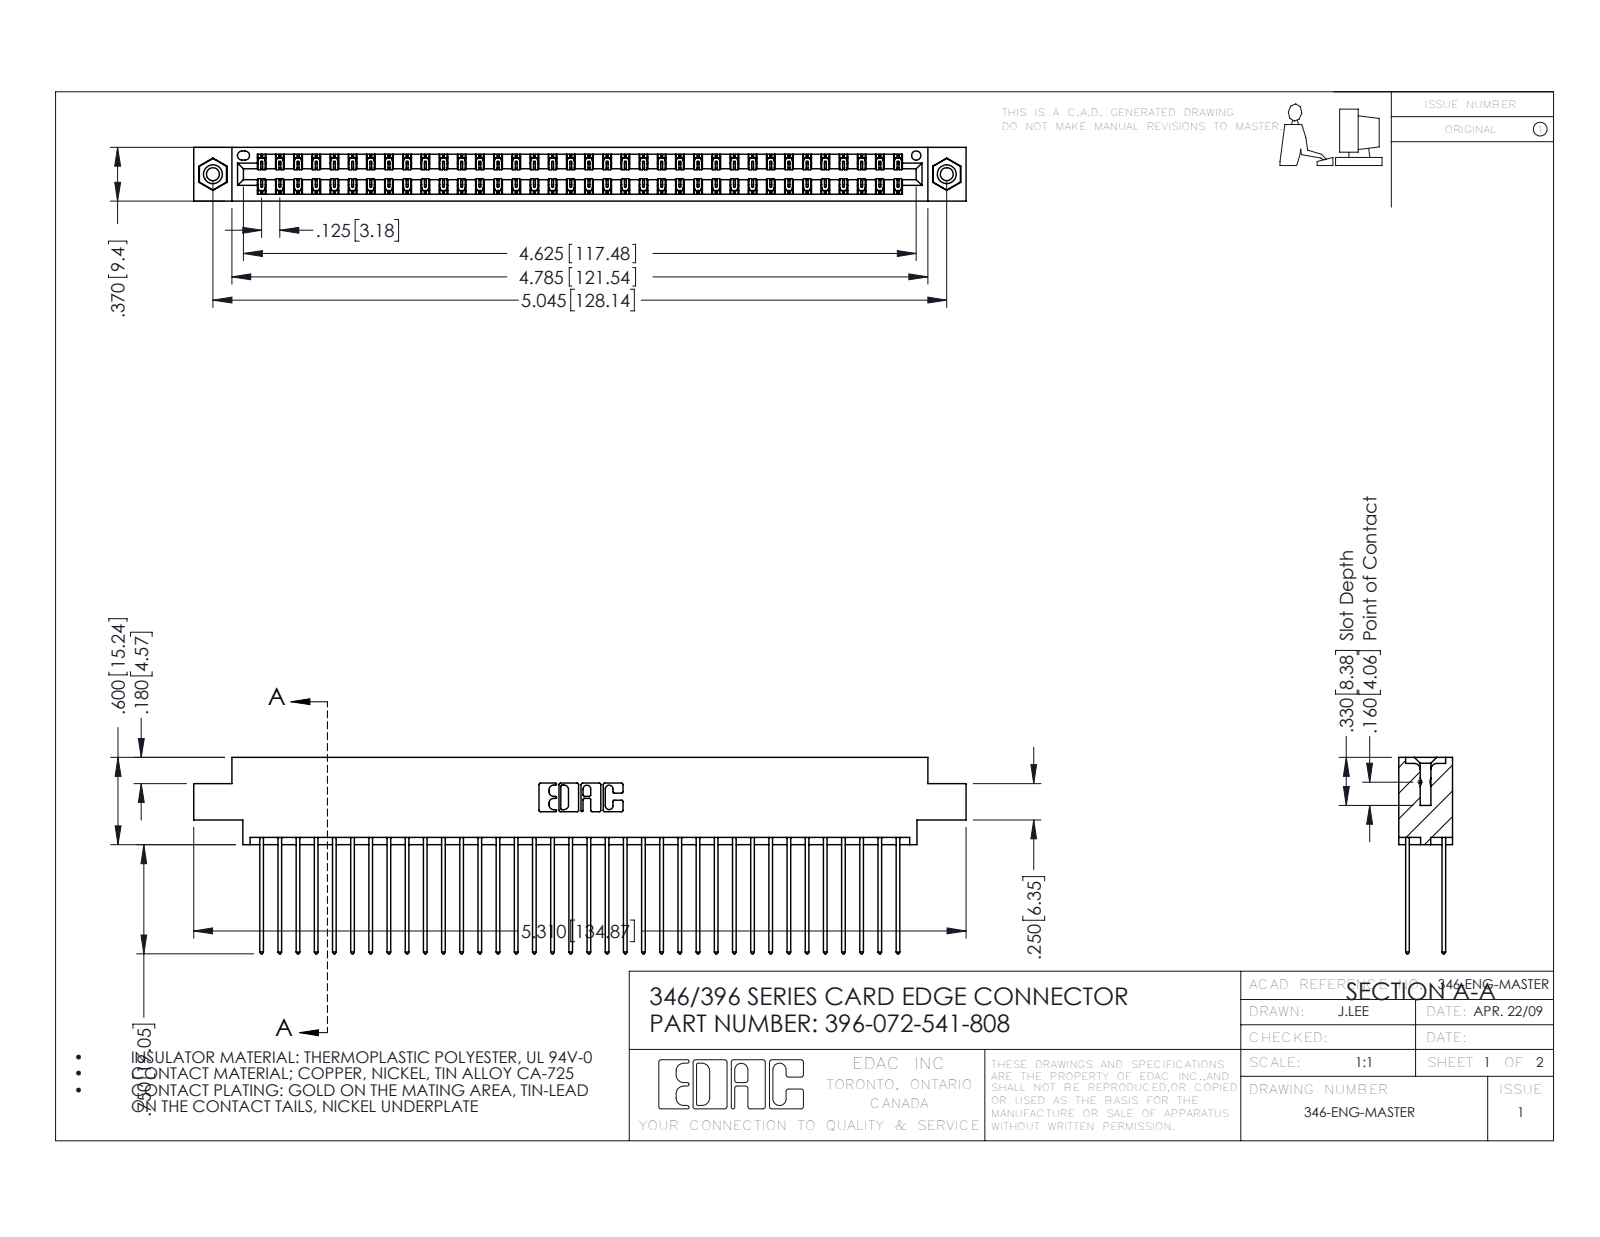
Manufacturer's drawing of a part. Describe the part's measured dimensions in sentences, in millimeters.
The part is named "396-072-541-808; 346 Part_0.170 Offset - 0.156 Dia-TI; 345-292-001_345-293-141; 345-250-001_345-250-003-102". Its 3-D file was written by "SolidWorks 2016 (CONFIG_CONTROL_DESIGN)". It is 75 solids with 3930 faces: 2632 planar, 1282 cylindrical and 16 other. Overall it measures 134.9 by 34.3 by 9.4 millimeters. Its volume is 13 400 cubic millimeters and its surface area 20 450 square millimeters. Round holes: 2 of diameter 2.3, 2 of diameter 3.2, 2 of diameter 4, 1 of diameter 1.6. Round bosses or shafts: 2 of diameter 3.9. Partial cylindrical surfaces (rounded edges, fillets, slot ends): 108 of radius 0.2, 72 of radius 0.3, 22 of radius 0.3, 6 of radius 0.2, 6 of radius 0.8, 3 of radius 0.7, 2 of radius 0.4, 2 of radius 0.6. The main face-to-face distances are 1.2, 8.2, 6.4, 1.8, 7.6, 0.6, 9.4, 7, 5.6, 5.7. The hole center spacings are 6.2, 122.8, 128.1.
